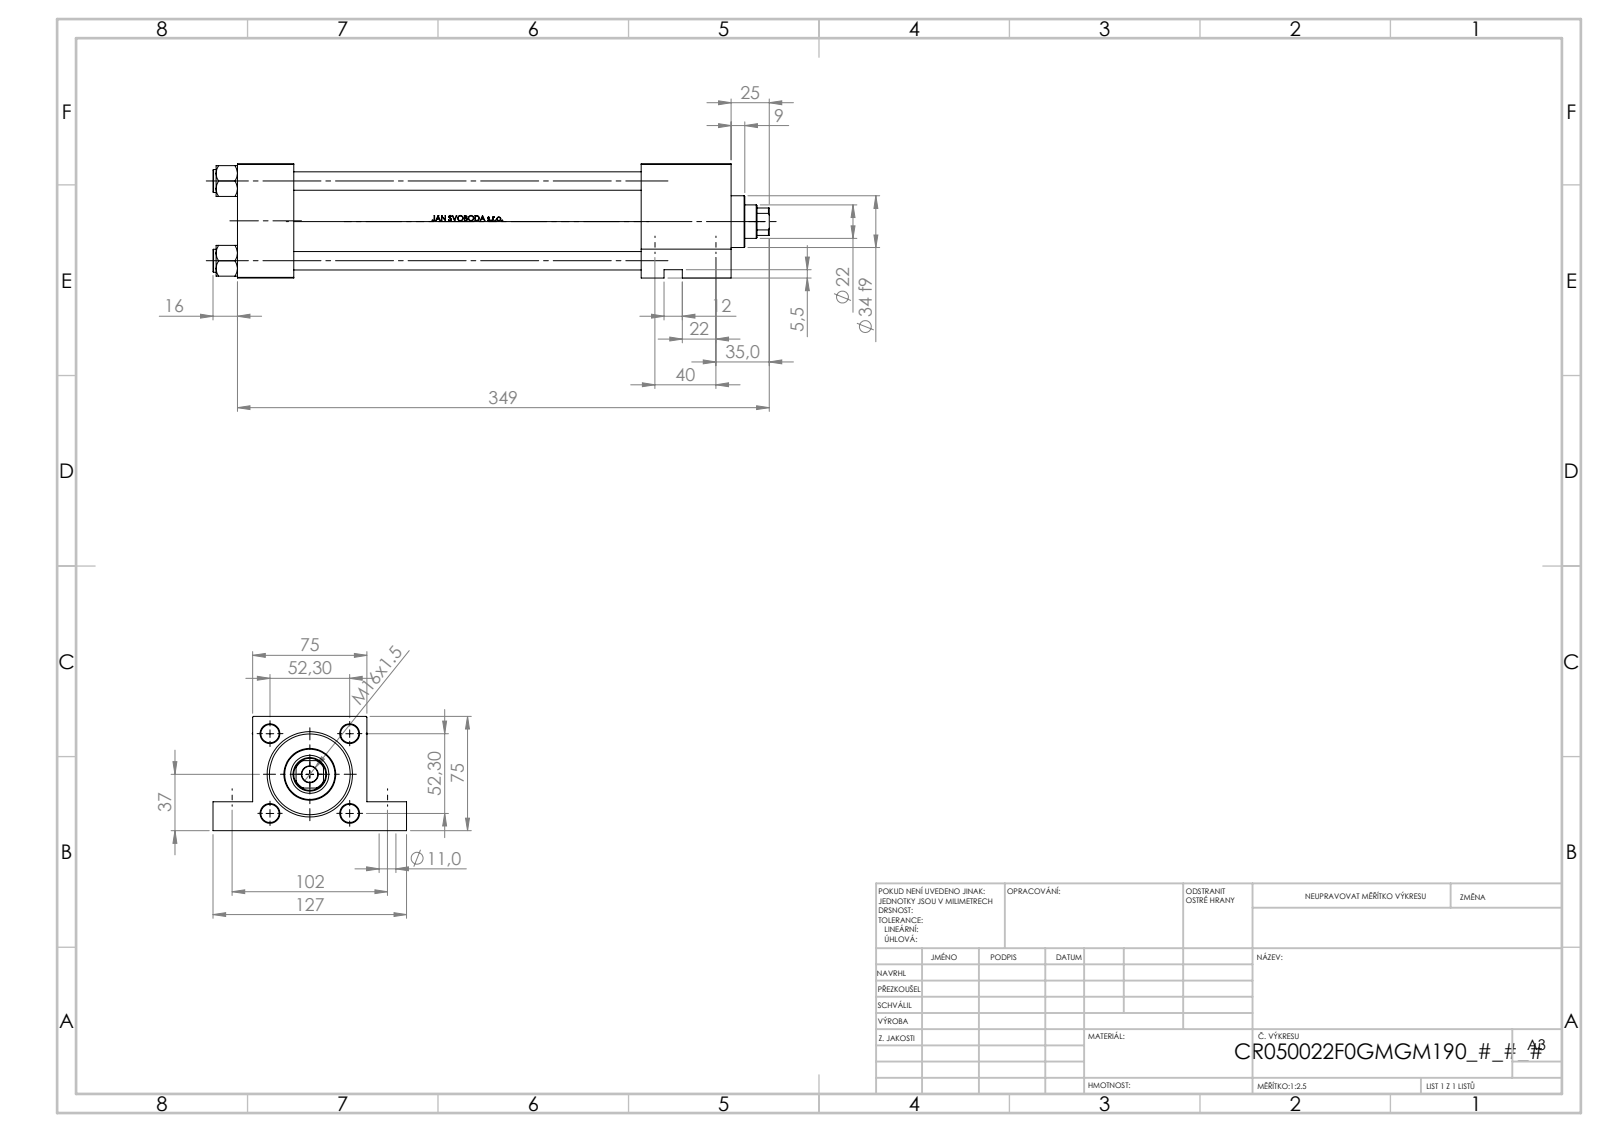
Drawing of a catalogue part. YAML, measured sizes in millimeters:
part_name: "NUT_M5_F; V215CR_F_Body; V215_VC_A; V215CR_VCP_F (+1 more)"
step_written_by: "SolidWorks 2019 (CONFIG_CONTROL_DESIGN)"
units: millimeters
bodies: {solids: 11, faces: 1103, planar: 437, cylindrical: 126, other: 540}
overall_size: [365, 127, 75]
volume: 933147
surface_area: 250347
round_holes:
  - {diameter: 11, count: 4}
  - {diameter: 12, count: 4}
  - {diameter: 7, count: 2}
  - {diameter: 30, count: 2}
  - {diameter: 10.5, count: 1}
  - {diameter: 17, count: 1}
  - {diameter: 20.96, count: 1}
  - {diameter: 22, count: 1}
  - {diameter: 25, count: 1}
  - {diameter: 41, count: 1}
  - {diameter: 50, count: 1}
  - {diameter: 53, count: 1}
round_bosses_or_shafts:
  - {diameter: 15, count: 4}
  - {diameter: 56, count: 1}
  - {diameter: 34, count: 1}
partial_cylinders:
  - {radius: 10.5, count: 1}
face_to_face_distances: [75, 37, 287, 324, 265, 228, 59, 295.3, 258.3, 30.3]
hole_center_spacings: [52.3, 36.63, 37.34, 40, 73.96, 102, 109.56, 263.5]
